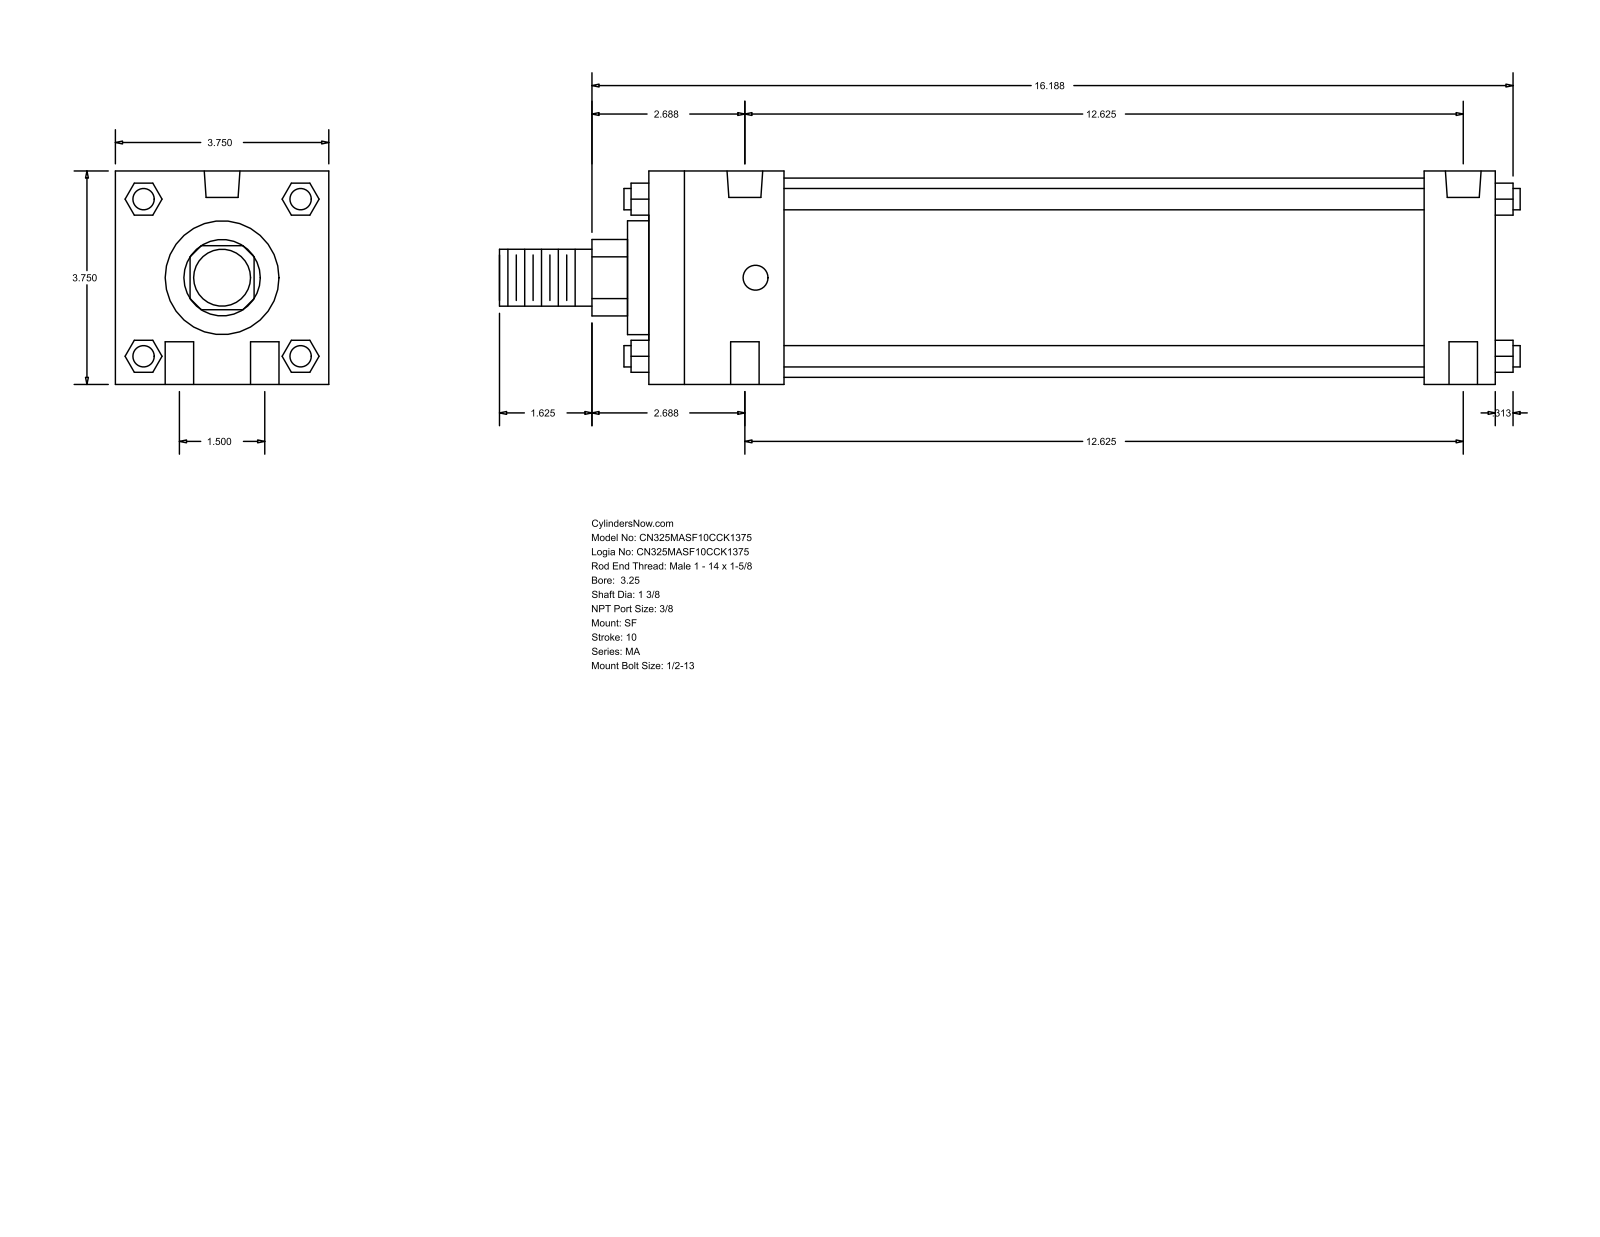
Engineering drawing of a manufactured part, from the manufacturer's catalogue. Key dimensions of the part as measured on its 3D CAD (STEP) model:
Part name (STEP PRODUCT): MA_SF__0325_1.375
STEP written by: GSSL Pune (CONFIG_CONTROL_DESIGN)
Units: millimetres
Bodies: 0 solids, 124 faces (94 planar, 30 cylindrical, 0 other)
Overall size (bounding box): 455.61 × 95.25 × 95.25
Round holes (diameter × count): ⌀12.7 ×4, ⌀11.11 ×2, ⌀15.93 ×2
Round bosses / shafts (diameter × count): ⌀9.53 ×4, ⌀88.9 ×1, ⌀50.8 ×1, ⌀34.92 ×1, ⌀25.4 ×1
Partial cylindrical surfaces — rounded edges, fillets, slot ends (radius × count): R17.06 ×1
Main face-to-face distances: 95.24, 377.83, 346.08, 31.75, 60.32, 285.76, 317.51, 9.52, 69.84, 355.6
Hole centre spacings: 19.05, 321.25, 320.68, 38.1, 322.94, 311.15
